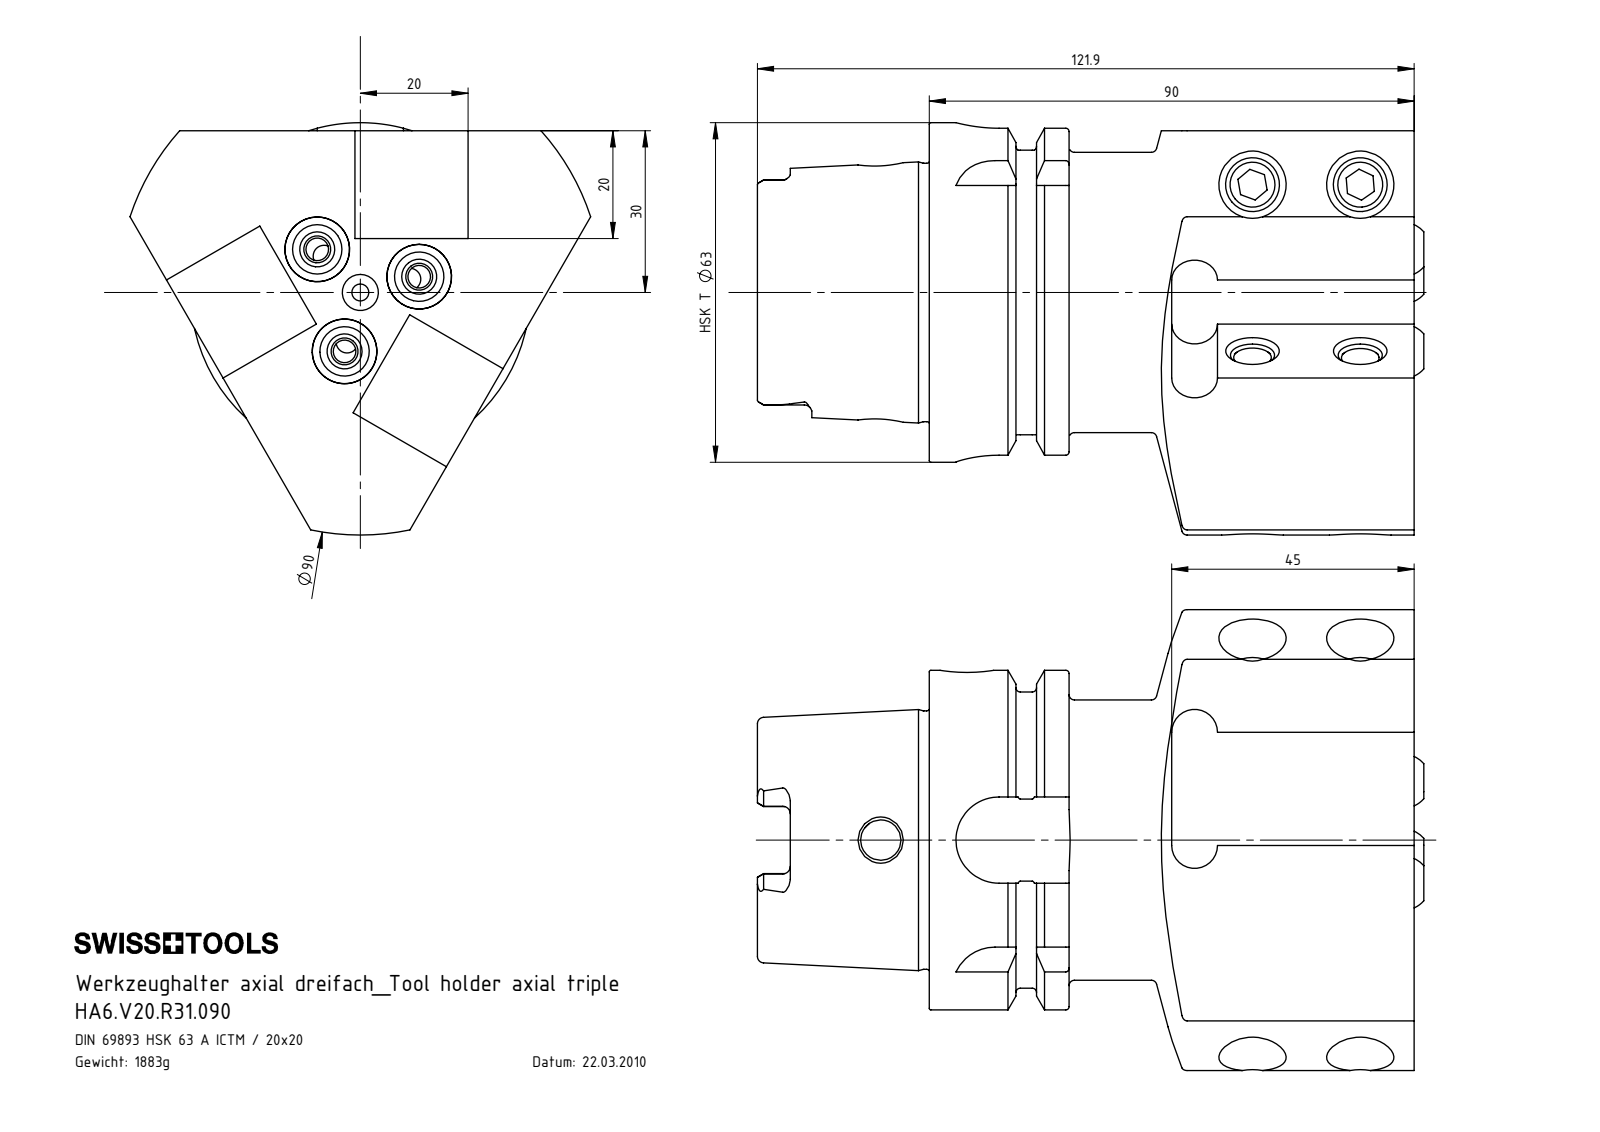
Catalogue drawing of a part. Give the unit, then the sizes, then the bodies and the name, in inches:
Units: inches
Overall size (bounding box): 4.87 × 3.366 × 3.012
Round holes (diameter × count): ⌀0.165 ×6, ⌀0.323 ×6, ⌀0.492 ×6, ⌀0.276 ×3, ⌀0.472 ×3, ⌀0.124 ×1, ⌀0.295 ×1, ⌀0.331 ×1, ⌀0.394 ×1, ⌀0.669 ×1, ⌀0.748 ×1, ⌀1.339 ×1
Round bosses / shafts (diameter × count): ⌀0.394 ×6, ⌀2.48 ×1, ⌀2.163 ×1, ⌀2.047 ×1, ⌀1.887 ×1
Partial cylindrical surfaces — rounded edges, fillets, slot ends (radius × count): R0.055 ×6, R0.167 ×6, R0.113 ×4, R0.315 ×4, R1.772 ×1
Main face-to-face distances: 0.787, 1.772, 0.827, 3.543, 1.022, 0.75, 2.522, 0.63, 0.315, 0.392
Hole centre spacings: 0.772, 0.787, 0.446, 0.445, 2.23, 2.98
Volume: 14.69 in³ · Surface area: 99.21 in²
Bodies: 13 solids, 392 faces (124 planar, 124 cylindrical, 144 other)
Part name (STEP PRODUCT): KU1-U12.001.010_1; HA6-V20.R31.090_C; HA6.V20.R31.090; ISO 4026 - M10 x 20 (+2 more)
STEP written by: SolidWorks 2017 (AUTOMOTIVE_DESIGN)
